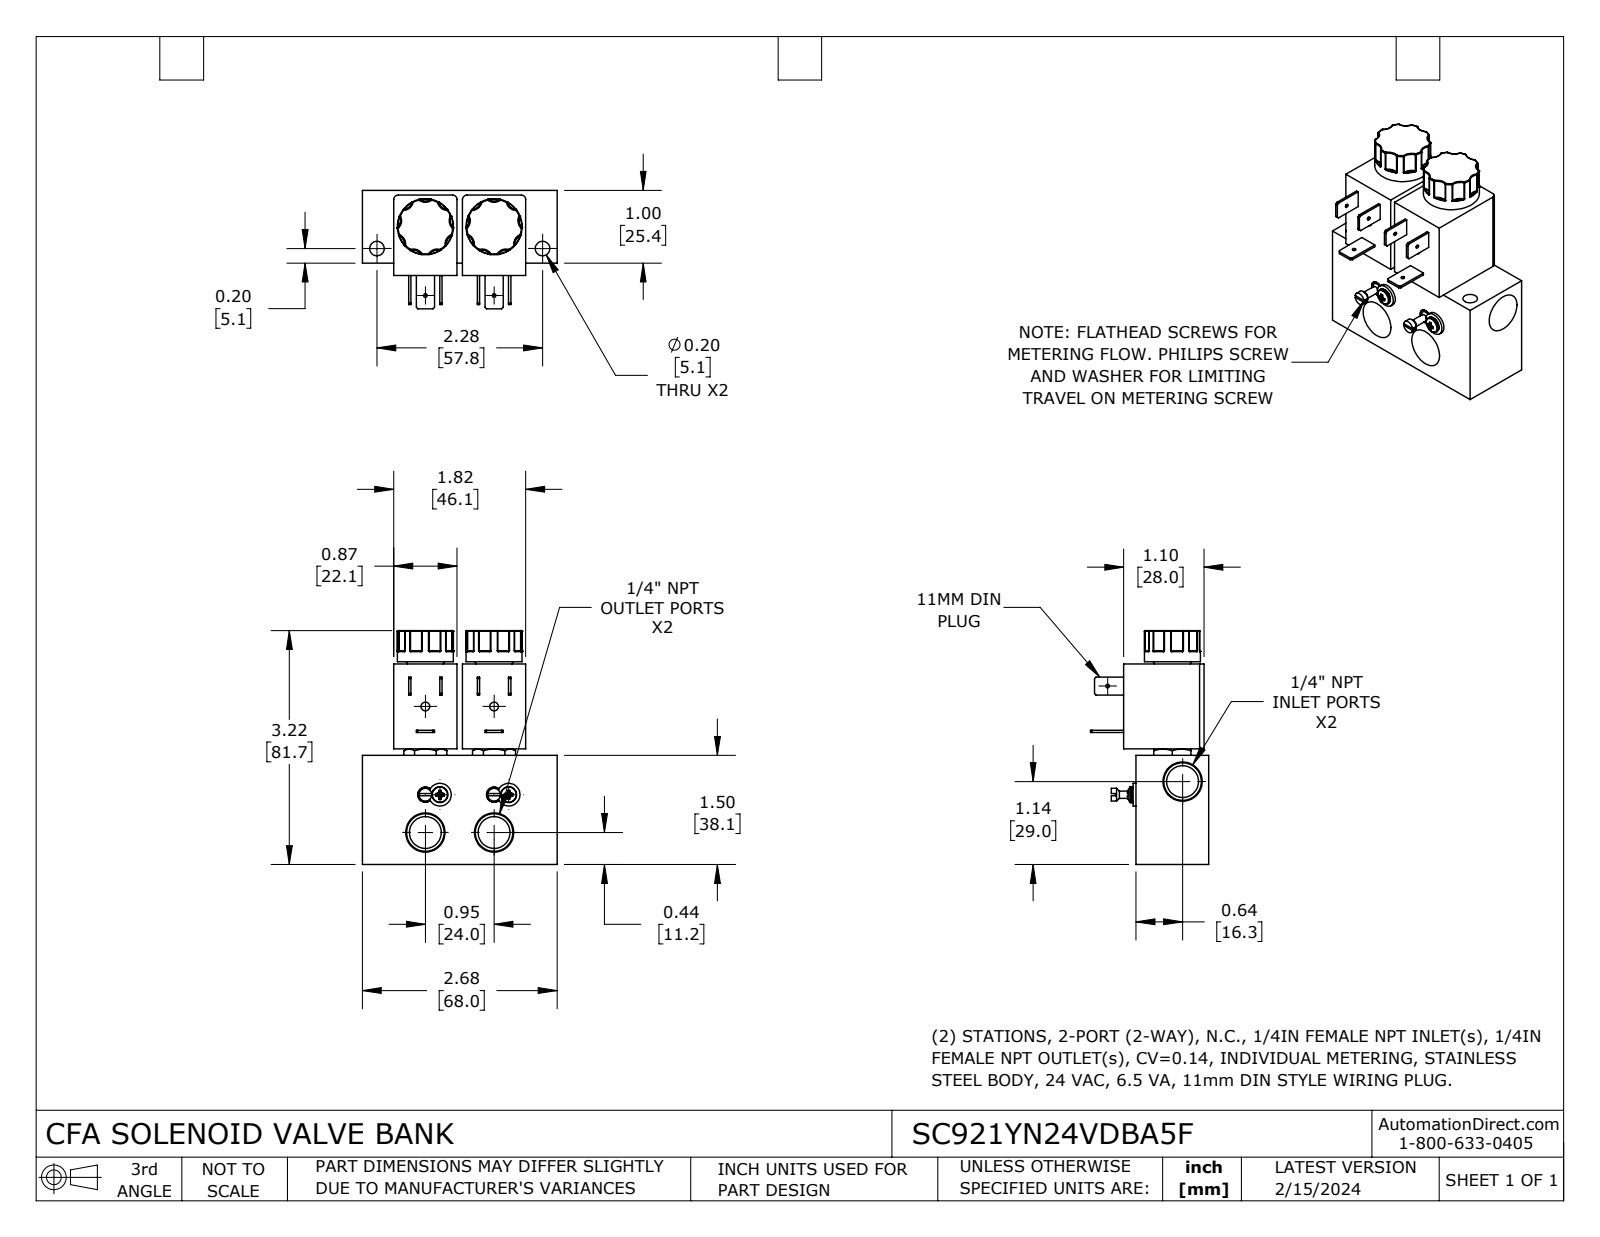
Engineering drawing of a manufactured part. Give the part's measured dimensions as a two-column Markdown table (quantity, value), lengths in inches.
| quantity | value |
| --- | --- |
| part name | SC921YN24VDBA5F |
| STEP written by | SolidWorks 2023 (CONFIG_CONTROL_DESIGN) |
| units | inches |
| bodies | 1 solid, 589 faces (156 planar, 152 cylindrical, 281 other) |
| overall size | 3.215 × 2.677 × 1.627 |
| volume | 6.159 in³ |
| surface area | 40.27 in² |
| round holes (diameter × count) | 0.05 × 3, 0.438 × 3, 0.12 × 2, 0.2 × 2, 0.208 × 2 |
| round bosses / shafts (diameter × count) | 0.77 × 2, 0.312 × 2, 0.219 × 2, 0.206 × 2, 0.175 × 2, 0.102 × 2, 0.1 × 2 |
| partial cylindrical surfaces (radius × count) | 0.01 × 36, 0.133 × 18, 0.06 × 4, 0.308 × 1 |
| main face-to-face distances | 1, 0.945, 0.431, 1.301, 1.376, 2.246, 0.87, 1.5, 1.169, 0.169 |
| hole center spacings | 0.945, 0.52, 0.928, 1.078, 1.212, 1.537, 1.732, 1.735 |
